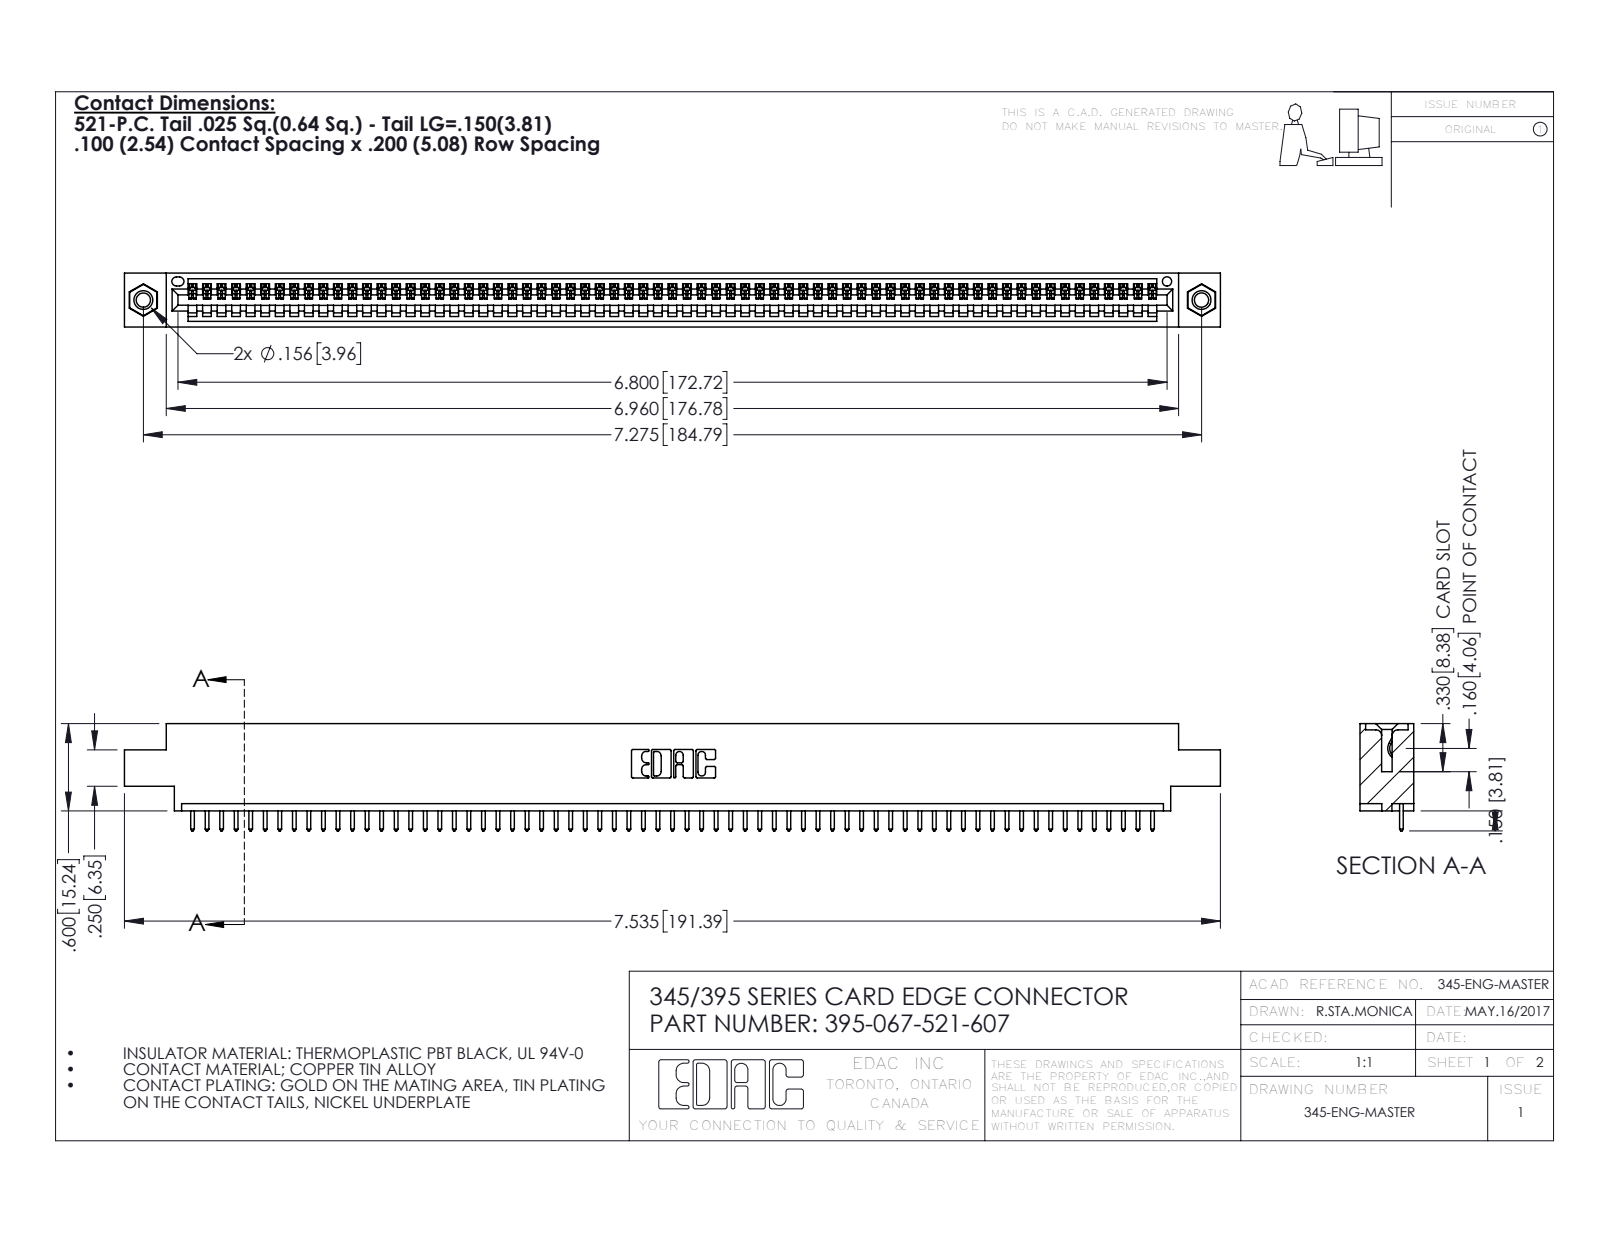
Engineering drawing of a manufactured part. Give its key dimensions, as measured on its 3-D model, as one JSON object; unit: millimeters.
{"part_name": "395-067-521-607; 345-292-001_345-293-121; 345-250-001_345-250-005-103; 345 Part_0.170 Offset - 0.156 Dia-TI", "step_written_by": "SolidWorks 2016 (CONFIG_CONTROL_DESIGN)", "units": "millimeters", "bodies": {"solids": 70, "faces": 4076, "planar": 2796, "cylindrical": 1264, "other": 16}, "overall_size": [191.4, 18.7, 9.4], "volume_mm3": 18060, "surface_area_mm2": 23760, "round_holes": [[2.5, 2], [3.2, 2], [4, 2], [1.6, 1]], "round_bosses_or_shafts": [[3.9, 2]], "partial_cylinders_radius": [[0.2, 134], [0.3, 134], [0.3, 22], [0.2, 6], [0.8, 6], [0.7, 3], [0.8, 2], [1, 2]], "face_to_face_distances": [1.8, 7.6, 9.4, 5.1, 2.5, 6.9, 0.6, 5.7, 4.4, 3.8], "hole_center_spacings": [6.9, 178.8, 184.8]}
